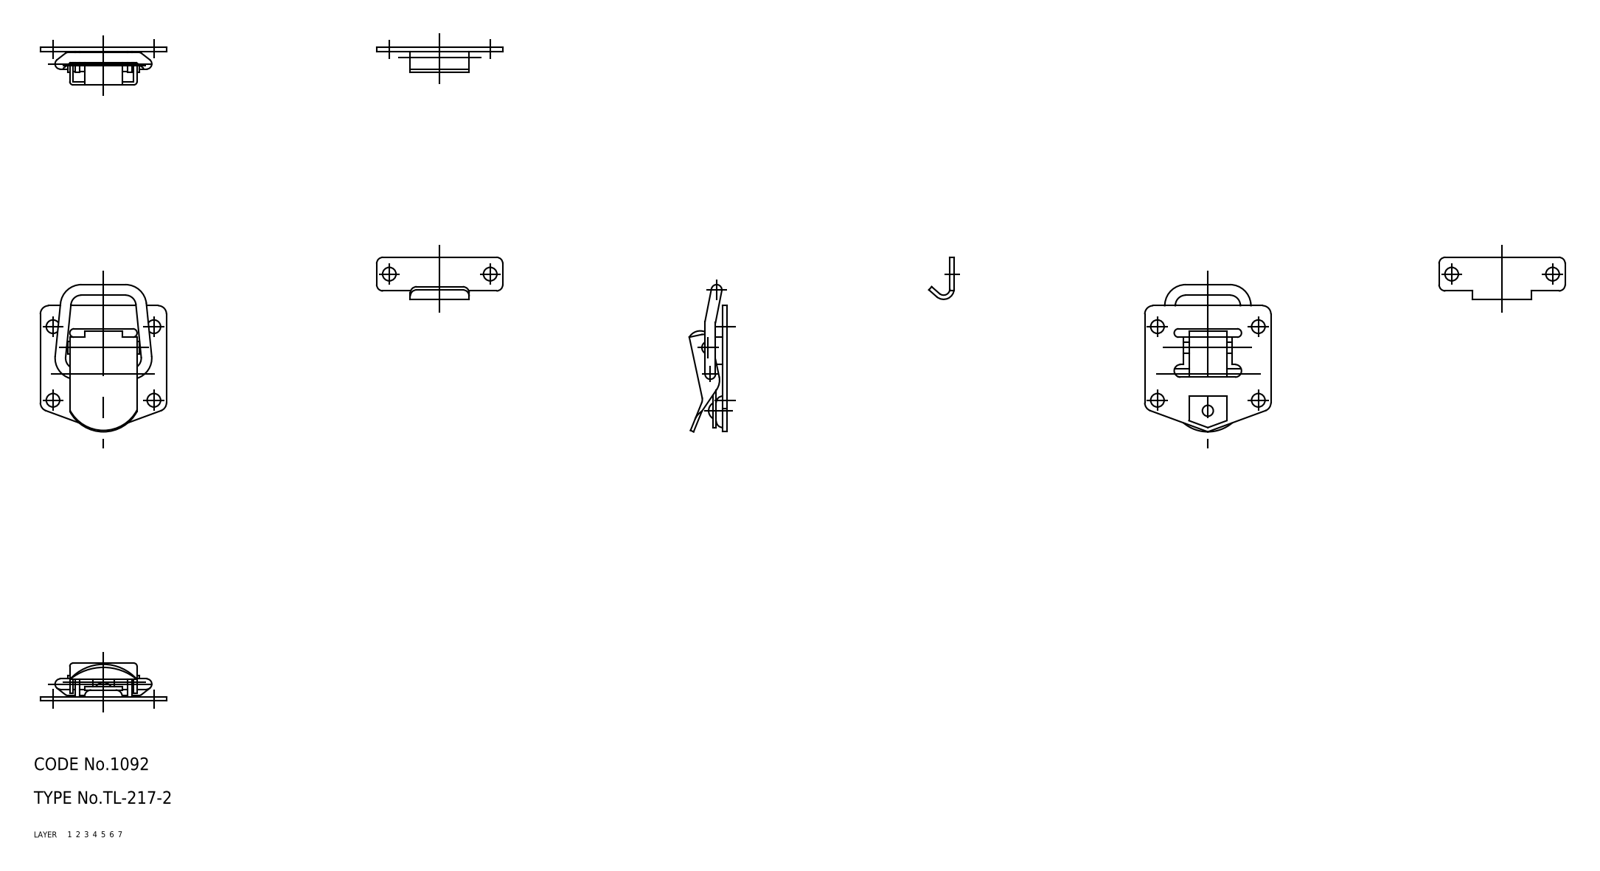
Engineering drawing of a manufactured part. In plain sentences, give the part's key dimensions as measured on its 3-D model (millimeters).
The part is named "shaft; rivet; lever; leaf spring (+4 more)". Its 3-D file was written by "CADfix (AUTOMOTIVE_DESIGN)". It is 7 solids with 200 faces: 0 planar, 0 cylindrical and 200 other. Overall it measures 41.5 by 30 by 9.02 millimeters. Its volume is 2 050 cubic millimeters and its surface area 4 693 square millimeters.
